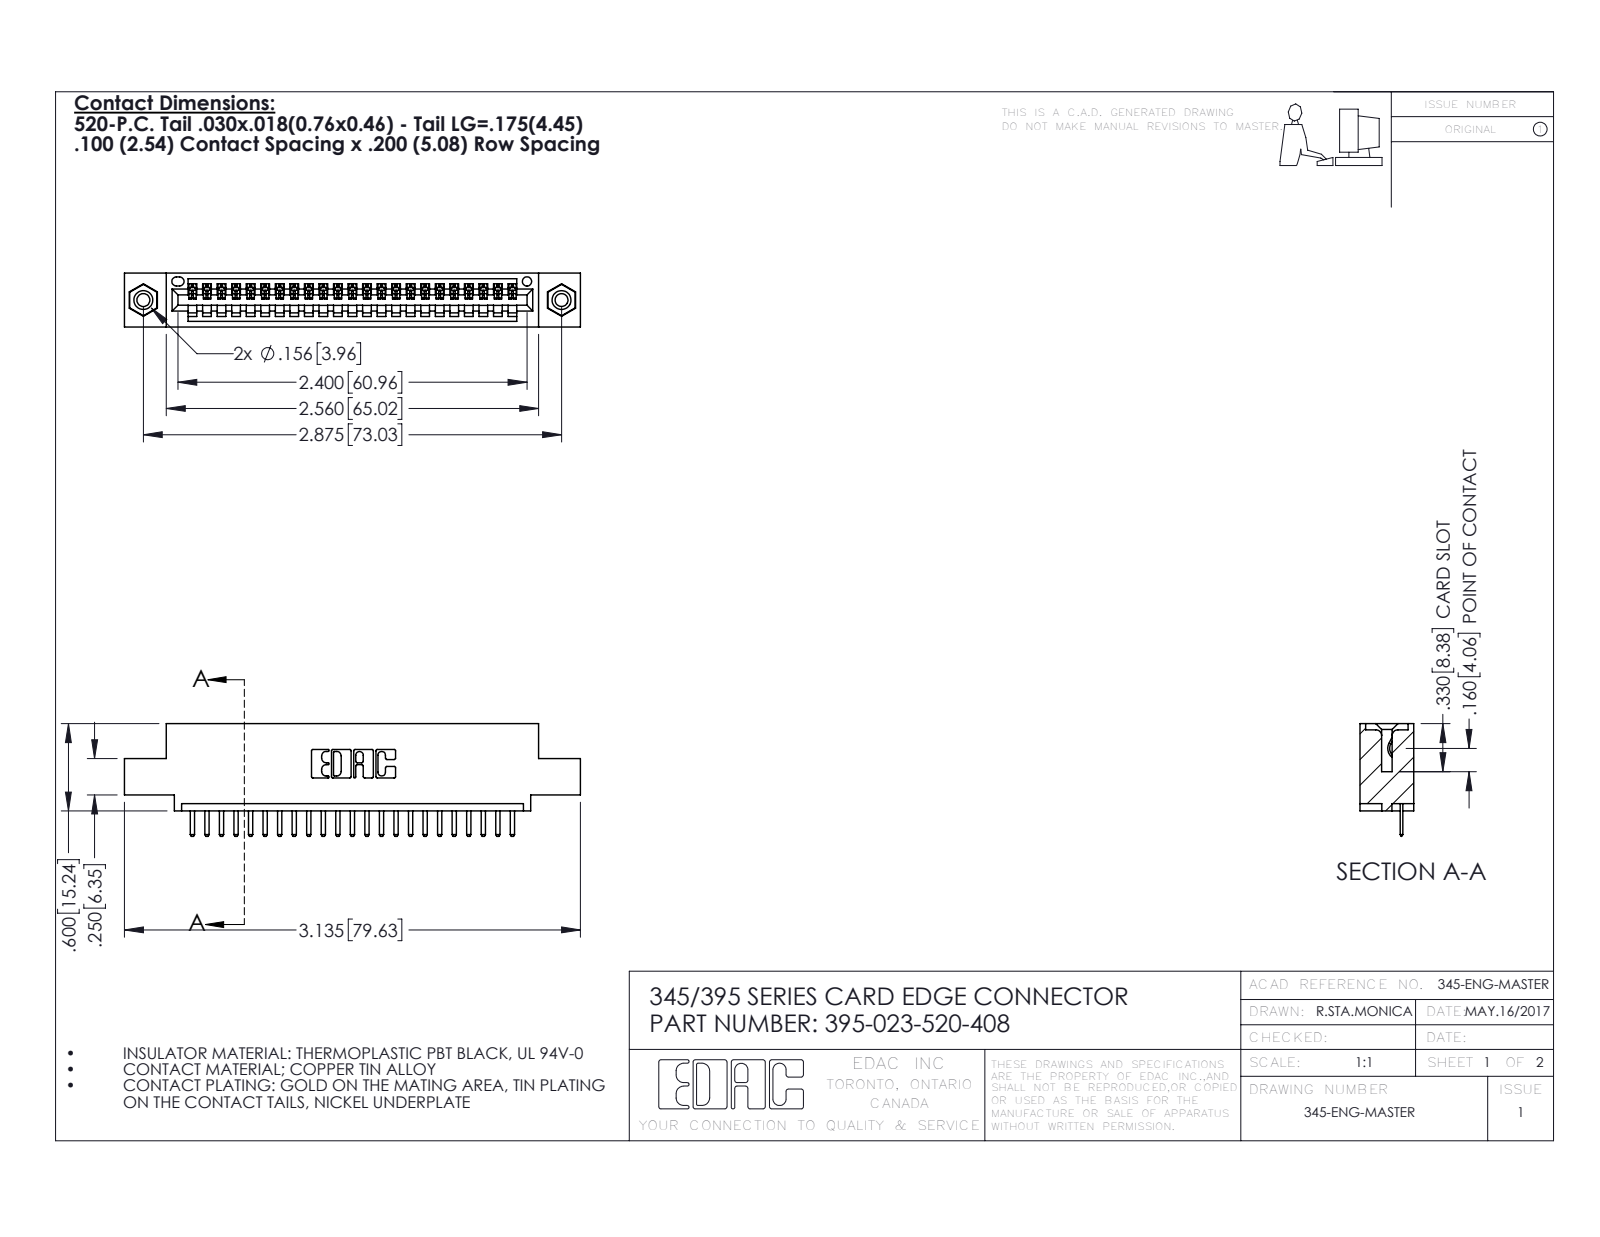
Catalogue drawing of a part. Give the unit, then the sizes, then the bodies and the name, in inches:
Units: inches
Overall size (bounding box): 3.135 × 0.775 × 0.37
Round holes (diameter × count): ⌀0.089 ×2, ⌀0.125 ×2, ⌀0.156 ×2, ⌀0.064 ×1
Round bosses / shafts (diameter × count): ⌀0.155 ×2
Partial cylindrical surfaces — rounded edges, fillets, slot ends (radius × count): R0.01 ×48, R0.006 ×46, R0.01 ×22, R0.007 ×6, R0.031 ×6, R0.026 ×3, R0.031 ×2, R0.04 ×2
Main face-to-face distances: 0.072, 0.298, 0.37, 0.2, 0.098, 0.272, 0.025, 0.225, 0.072, 0.149
Hole centre spacings: 0.27, 2.641, 2.875
Volume: 0.443 in³ · Surface area: 14.38 in²
Bodies: 26 solids, 1616 faces (1082 planar, 518 cylindrical, 16 other)
Part name (STEP PRODUCT): 345 Part_0.110 Offset - 0.156 Dia-TI; 395-023-520-408; 345-250-001_345-250-003-102; 345-292-001_345-293-120
STEP written by: SolidWorks 2016 (CONFIG_CONTROL_DESIGN)
